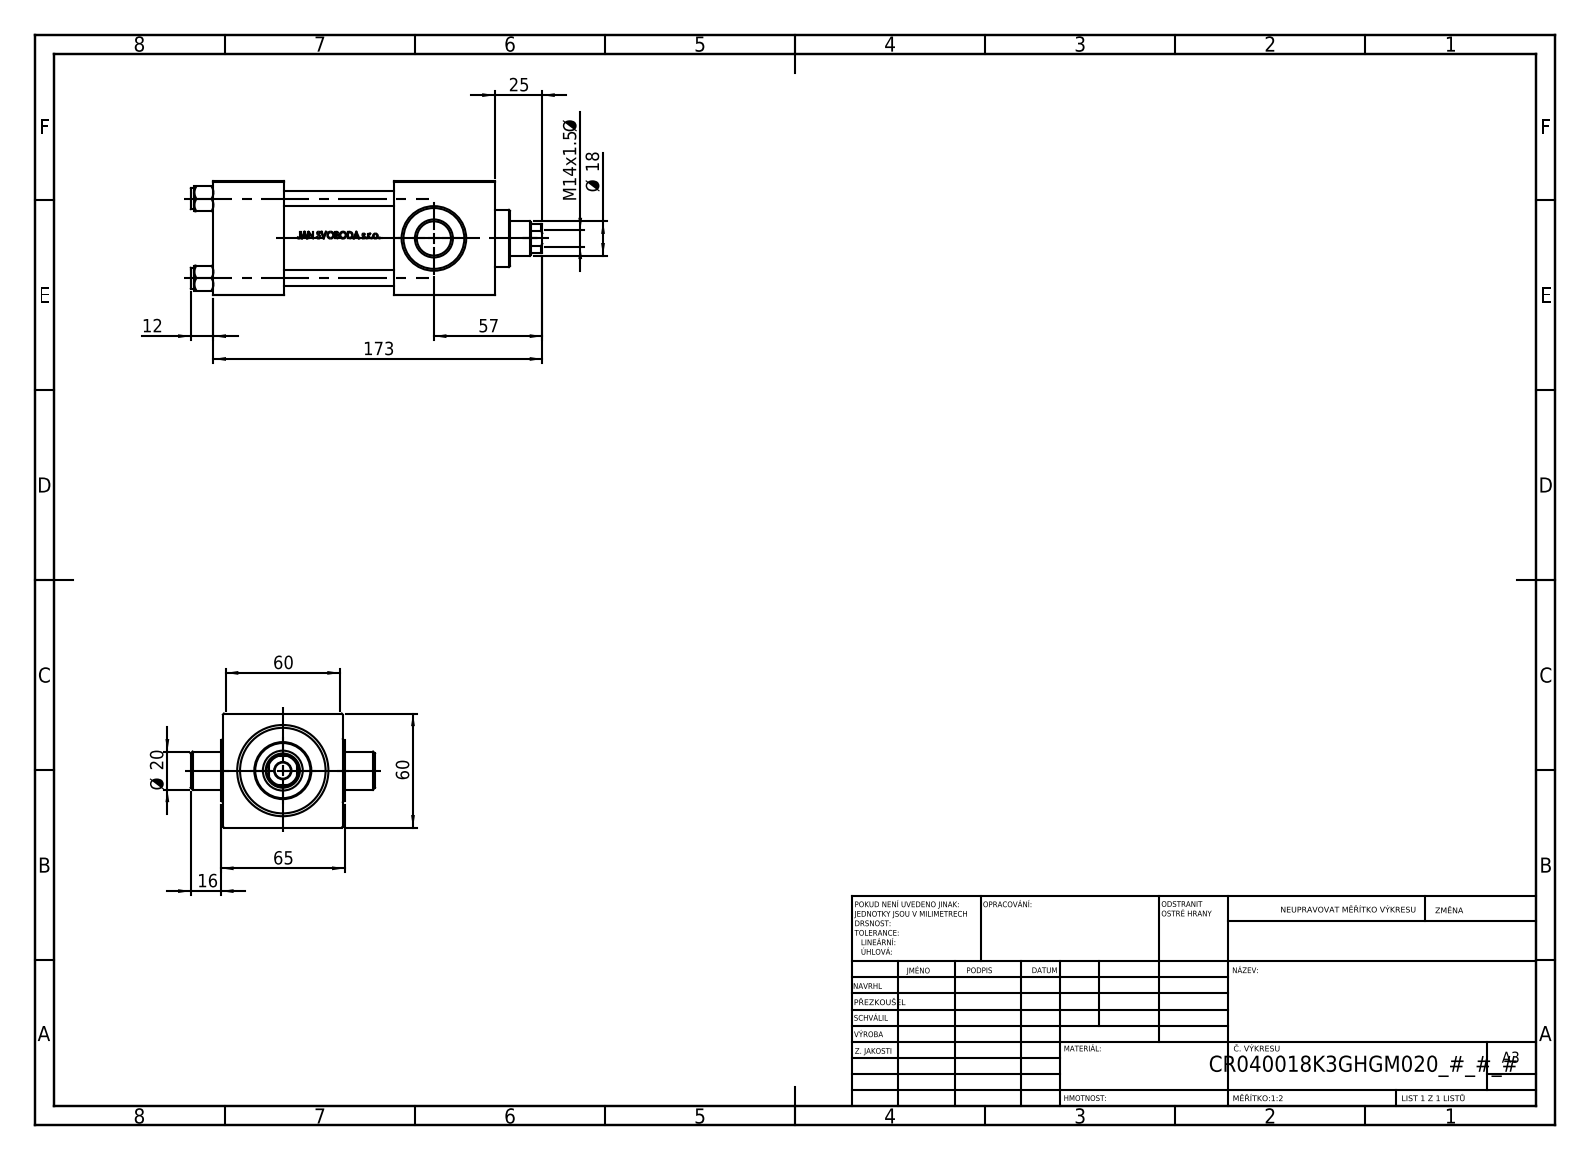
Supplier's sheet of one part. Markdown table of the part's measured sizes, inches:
| quantity | value |
| --- | --- |
| part name | V215_VC_A; V215CR_K_TYCINKA; NUT_M5_K; V215CR_VCP_K (+1 more) |
| STEP written by | SolidWorks 2019 (CONFIG_CONTROL_DESIGN) |
| units | inches |
| bodies | 11 solids, 1059 faces (427 planar, 110 cylindrical, 522 other) |
| overall size | 7.283 × 3.819 × 2.362 |
| volume | 26.35 in³ |
| surface area | 160.5 in² |
| round holes (diameter × count) | 0.315 × 4, 0.276 × 1, 0.335 × 1, 0.709 × 1, 0.827 × 1, 1.22 × 1, 1.575 × 1, 1.772 × 1 |
| round bosses / shafts (diameter × count) | 0.433 × 4, 1.811 × 1, 1.181 × 1, 0.787 × 1 |
| partial cylindrical surfaces (radius × count) | 0.335 × 1 |
| main face-to-face distances | 2.362, 0.059, 2.421, 1.457, 5.827, 4.37, 3.74, 2.283, 2.087, 2.48 |
| hole center spacings | 1.161, 1.642, 2.322 |
